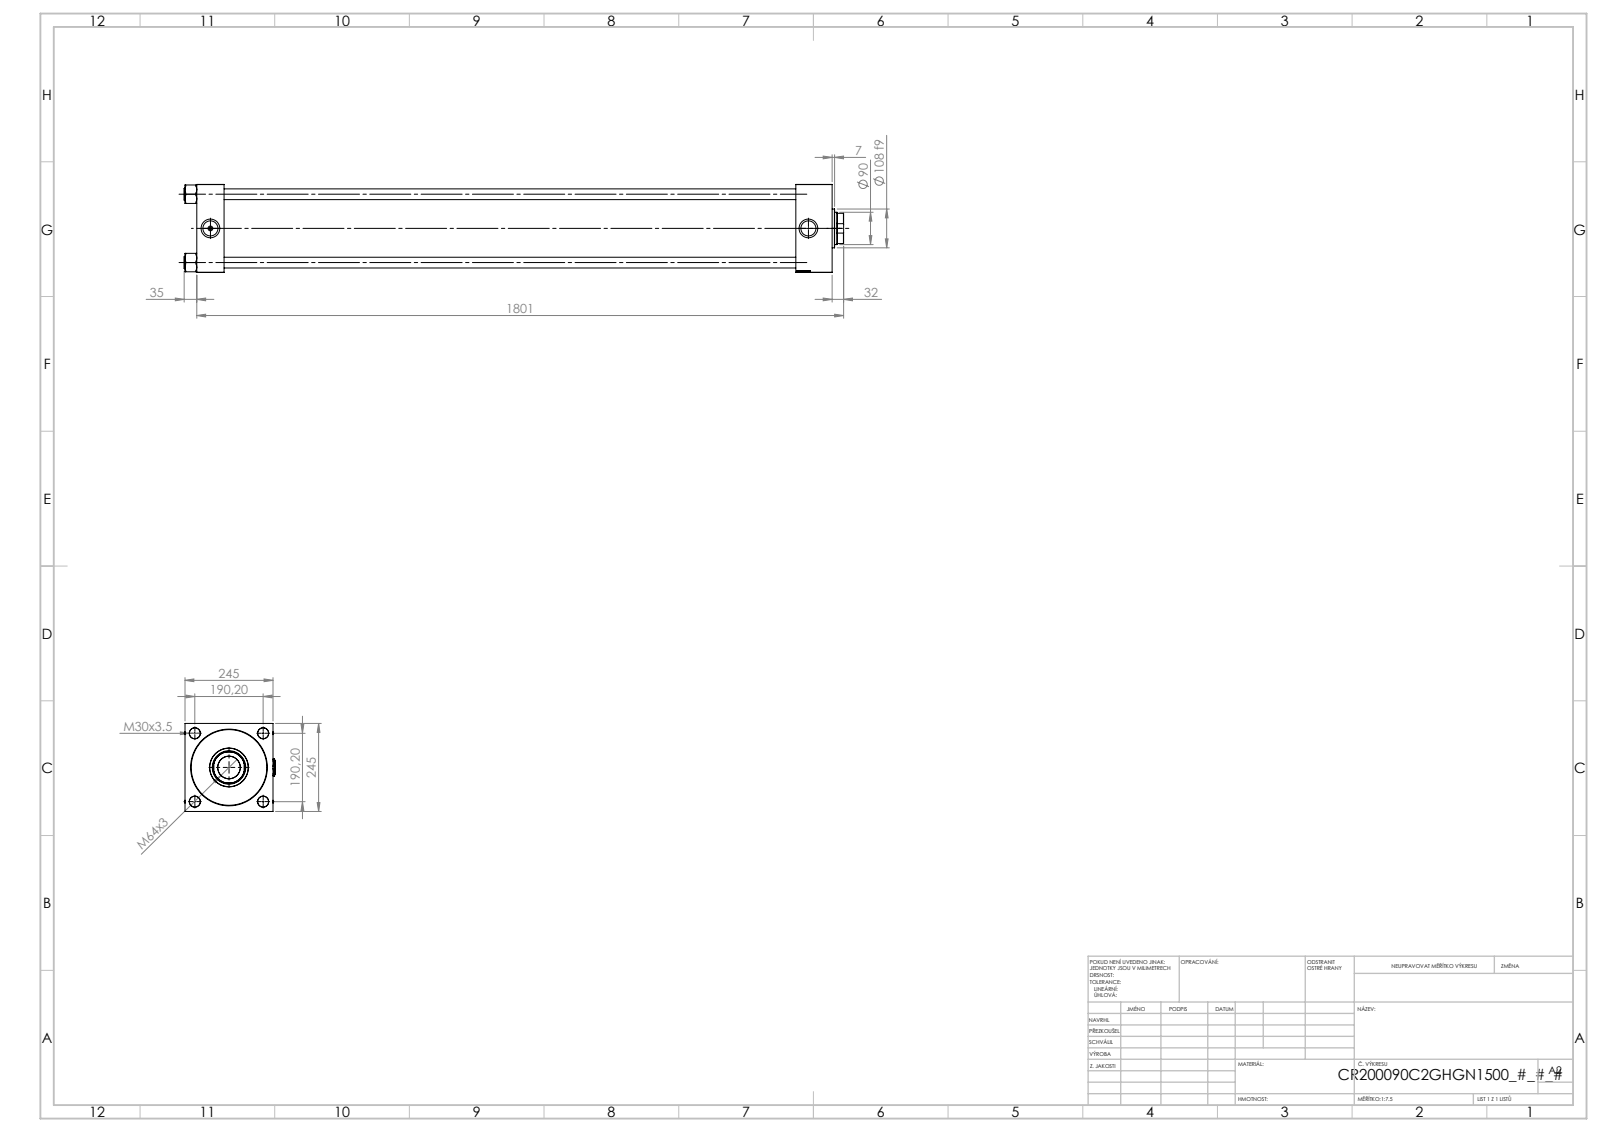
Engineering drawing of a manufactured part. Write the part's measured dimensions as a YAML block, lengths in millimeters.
part_name: "V215_VC_A; V215CR_C_TYCINKA; Zatka_pro_OIL_PORT; NUT_M5_C (+2 more)"
step_written_by: "SolidWorks 2019 (CONFIG_CONTROL_DESIGN)"
units: millimeters
bodies: {solids: 12, faces: 1250, planar: 598, cylindrical: 94, other: 558}
overall_size: [1836, 254.22, 245]
volume: 29870000
surface_area: 3911000
round_holes:
  - {diameter: 30, count: 4}
  - {diameter: 7, count: 2}
  - {diameter: 41.92, count: 2}
  - {diameter: 52, count: 2}
  - {diameter: 62.5, count: 1}
  - {diameter: 90, count: 1}
  - {diameter: 93, count: 1}
  - {diameter: 146, count: 1}
  - {diameter: 200, count: 1}
  - {diameter: 210.5, count: 1}
round_bosses_or_shafts:
  - {diameter: 33, count: 4}
  - {diameter: 206, count: 1}
  - {diameter: 108, count: 1}
partial_cylinders:
  - {radius: 44, count: 1}
face_to_face_distances: [245, 76, 1769, 1693, 1740.3, 1664.3, 28.7, 1668, 1592, 72.3]
hole_center_spacings: [134.49, 190.2, 268.98, 1665]
